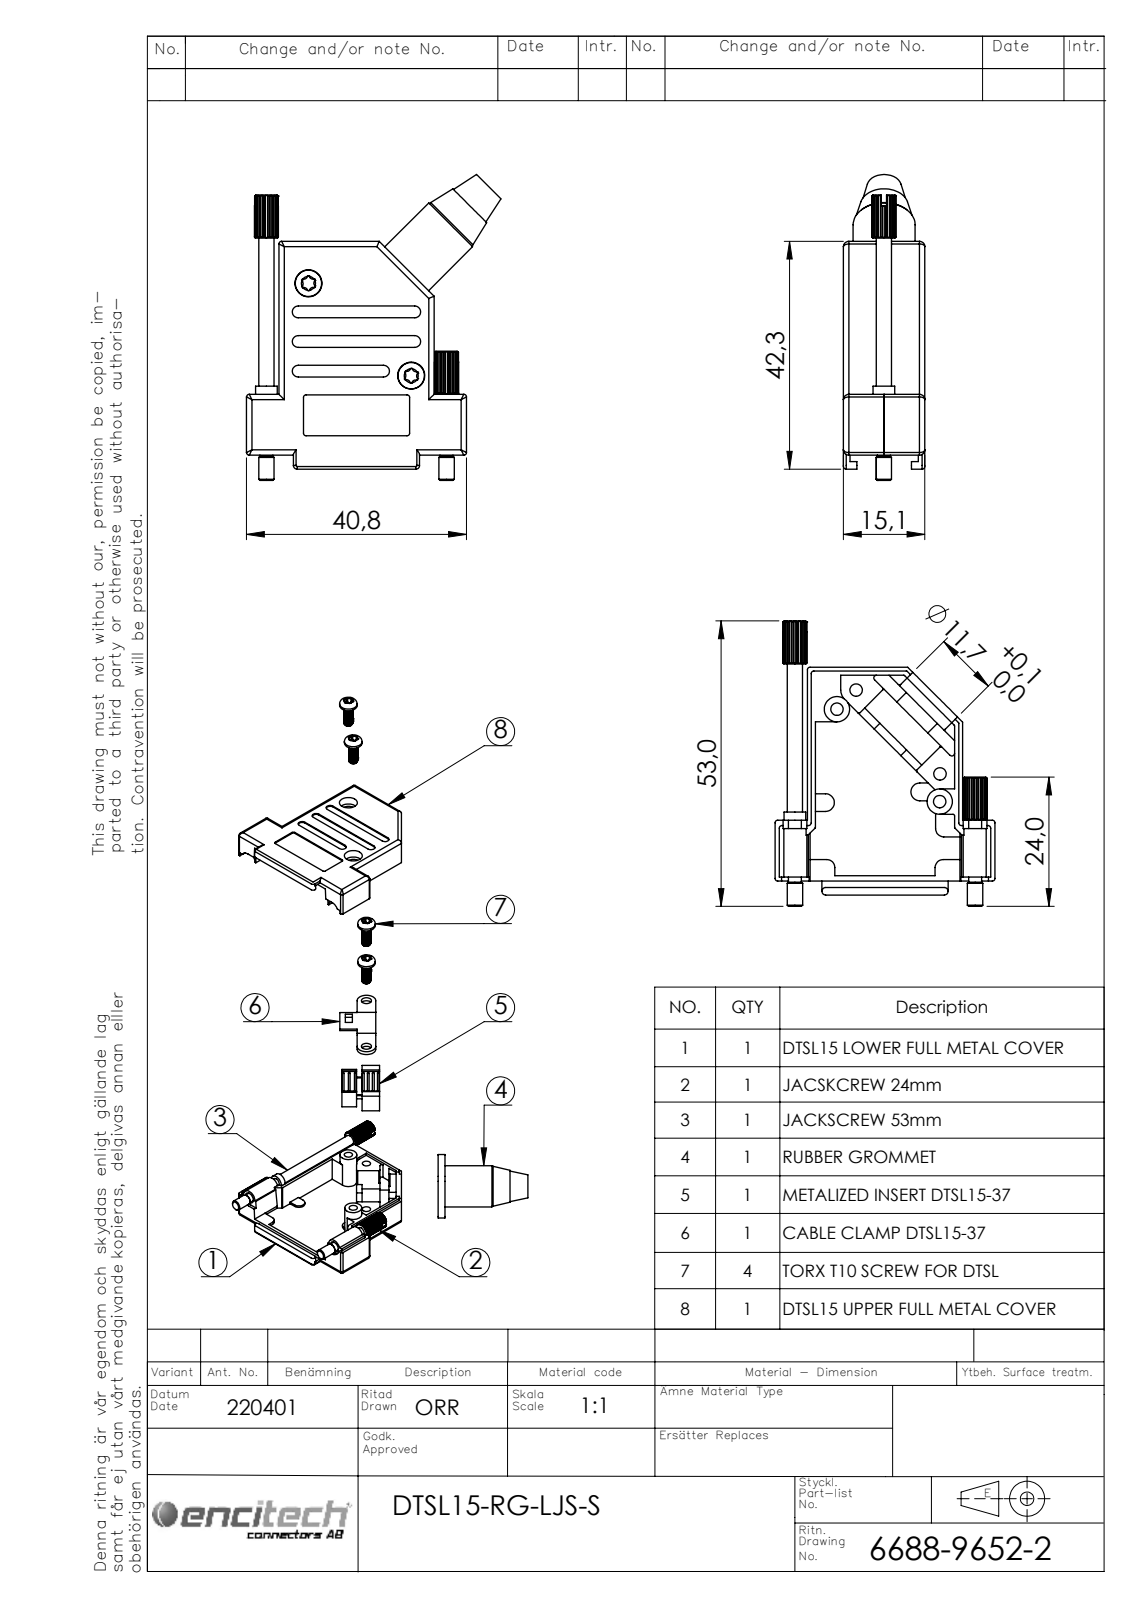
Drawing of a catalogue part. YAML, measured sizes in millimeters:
part_name: "6838-0111-32; 6844-0104-01; 6826-0147-01; 6826-0147-02 (+5 more)"
step_written_by: "SolidWorks 2021 (AUTOMOTIVE_DESIGN)"
units: millimeters
bodies: {solids: 15, faces: 1038, planar: 442, cylindrical: 508, other: 88}
overall_size: [56.8, 47.2, 15.4]
volume: 9512
surface_area: 13645
round_holes:
  - {diameter: 2.3, count: 4}
  - {diameter: 2.8, count: 4}
  - {diameter: 3.1, count: 2}
  - {diameter: 5, count: 2}
  - {diameter: 4.4, count: 1}
  - {diameter: 9, count: 1}
  - {diameter: 11.7, count: 1}
round_bosses_or_shafts:
  - {diameter: 4.9, count: 4}
  - {diameter: 2.5, count: 4}
  - {diameter: 5.7, count: 2}
  - {diameter: 4.7, count: 2}
  - {diameter: 2.84, count: 2}
  - {diameter: 2.4, count: 2}
  - {diameter: 11.5, count: 1}
  - {diameter: 11.1, count: 1}
partial_cylinders:
  - {radius: 0.7, count: 26}
  - {radius: 0.18, count: 24}
  - {radius: 0.5, count: 24}
  - {radius: 1, count: 22}
  - {radius: 0.3, count: 10}
  - {radius: 1.1, count: 7}
  - {radius: 0.25, count: 4}
  - {radius: 1.5, count: 4}
face_to_face_distances: [1.35, 13.75, 15.1, 12.4, 1.5, 1.05, 6.2, 7.55, 14.8, 13.45]
hole_center_spacings: [5.03, 5.13, 5.15, 22.01, 22.57, 25.63, 25.64, 25.86]
